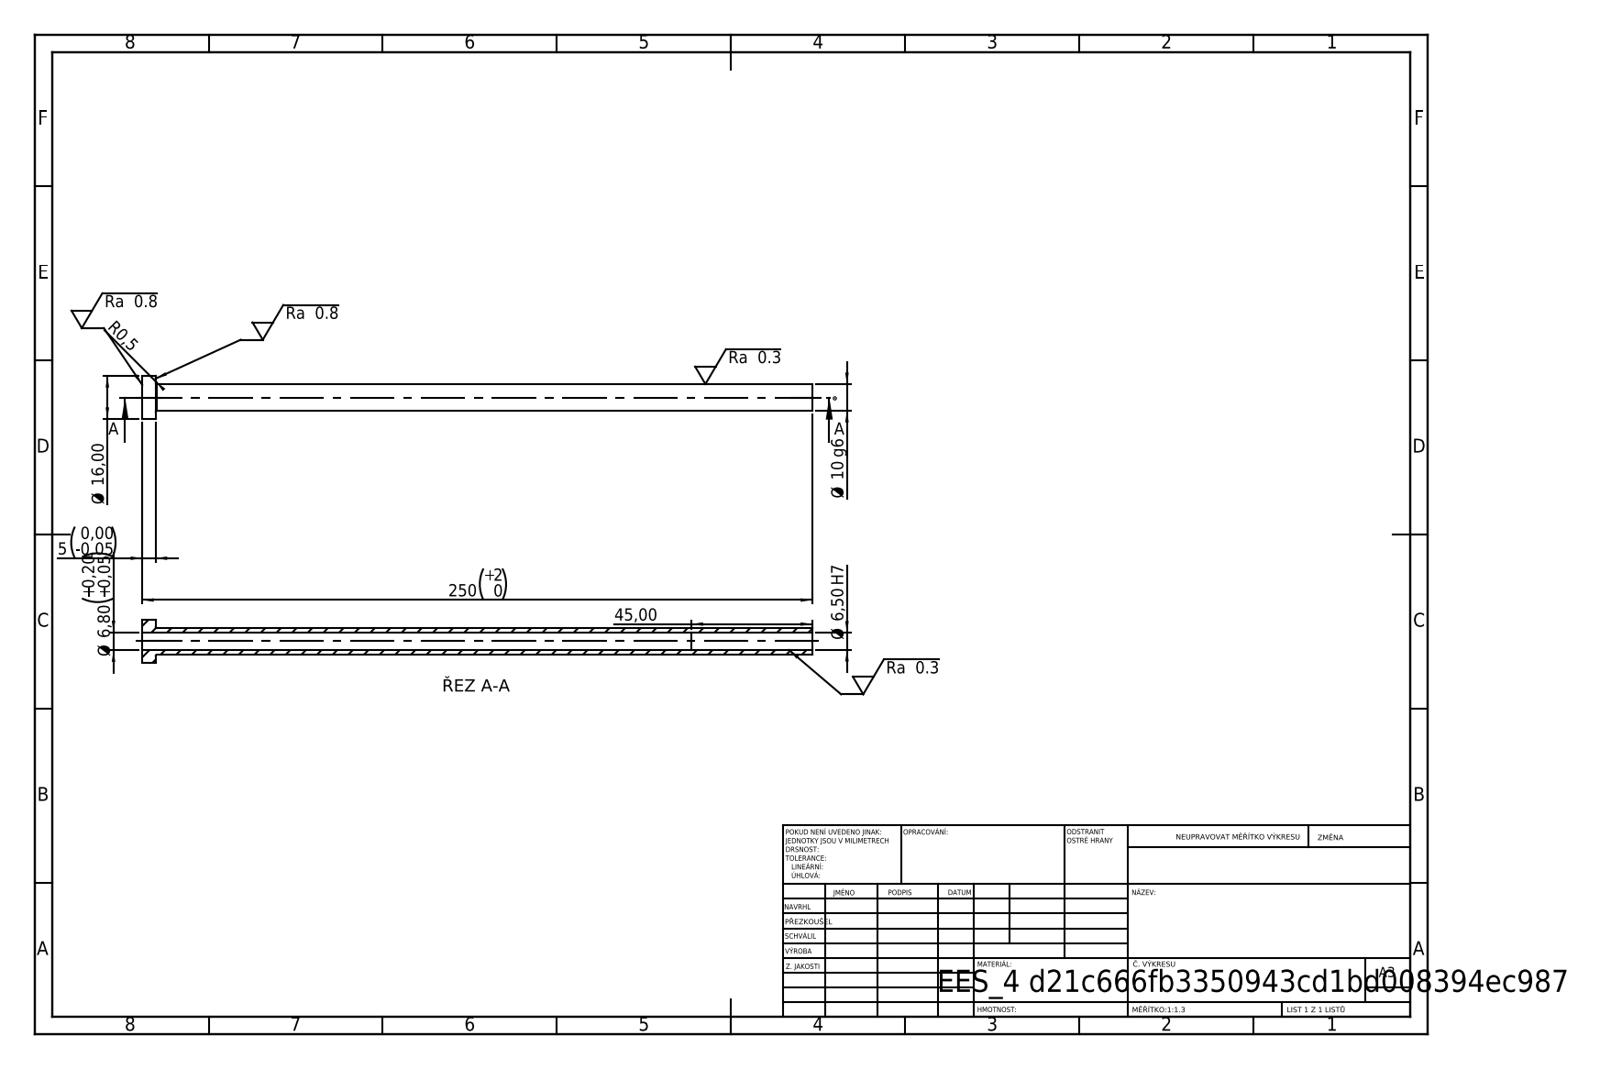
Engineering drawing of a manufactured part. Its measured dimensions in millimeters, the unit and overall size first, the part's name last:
Units: millimetres
Overall size (bounding box): 250 × 16 × 16
Round holes (diameter × count): ⌀6.5 ×1, ⌀6.8 ×1
Round bosses / shafts (diameter × count): ⌀16 ×1, ⌀10 ×1
Main face-to-face distances: 5, 250, 245, 205, 200, 45
Volume: 11 311 mm³ · Surface area: 13 576 mm²
Bodies: 1 solid, 14 faces (4 planar, 8 cylindrical, 2 other)
STEP written by: SolidWorks 2019 (CONFIG_CONTROL_DESIGN)
